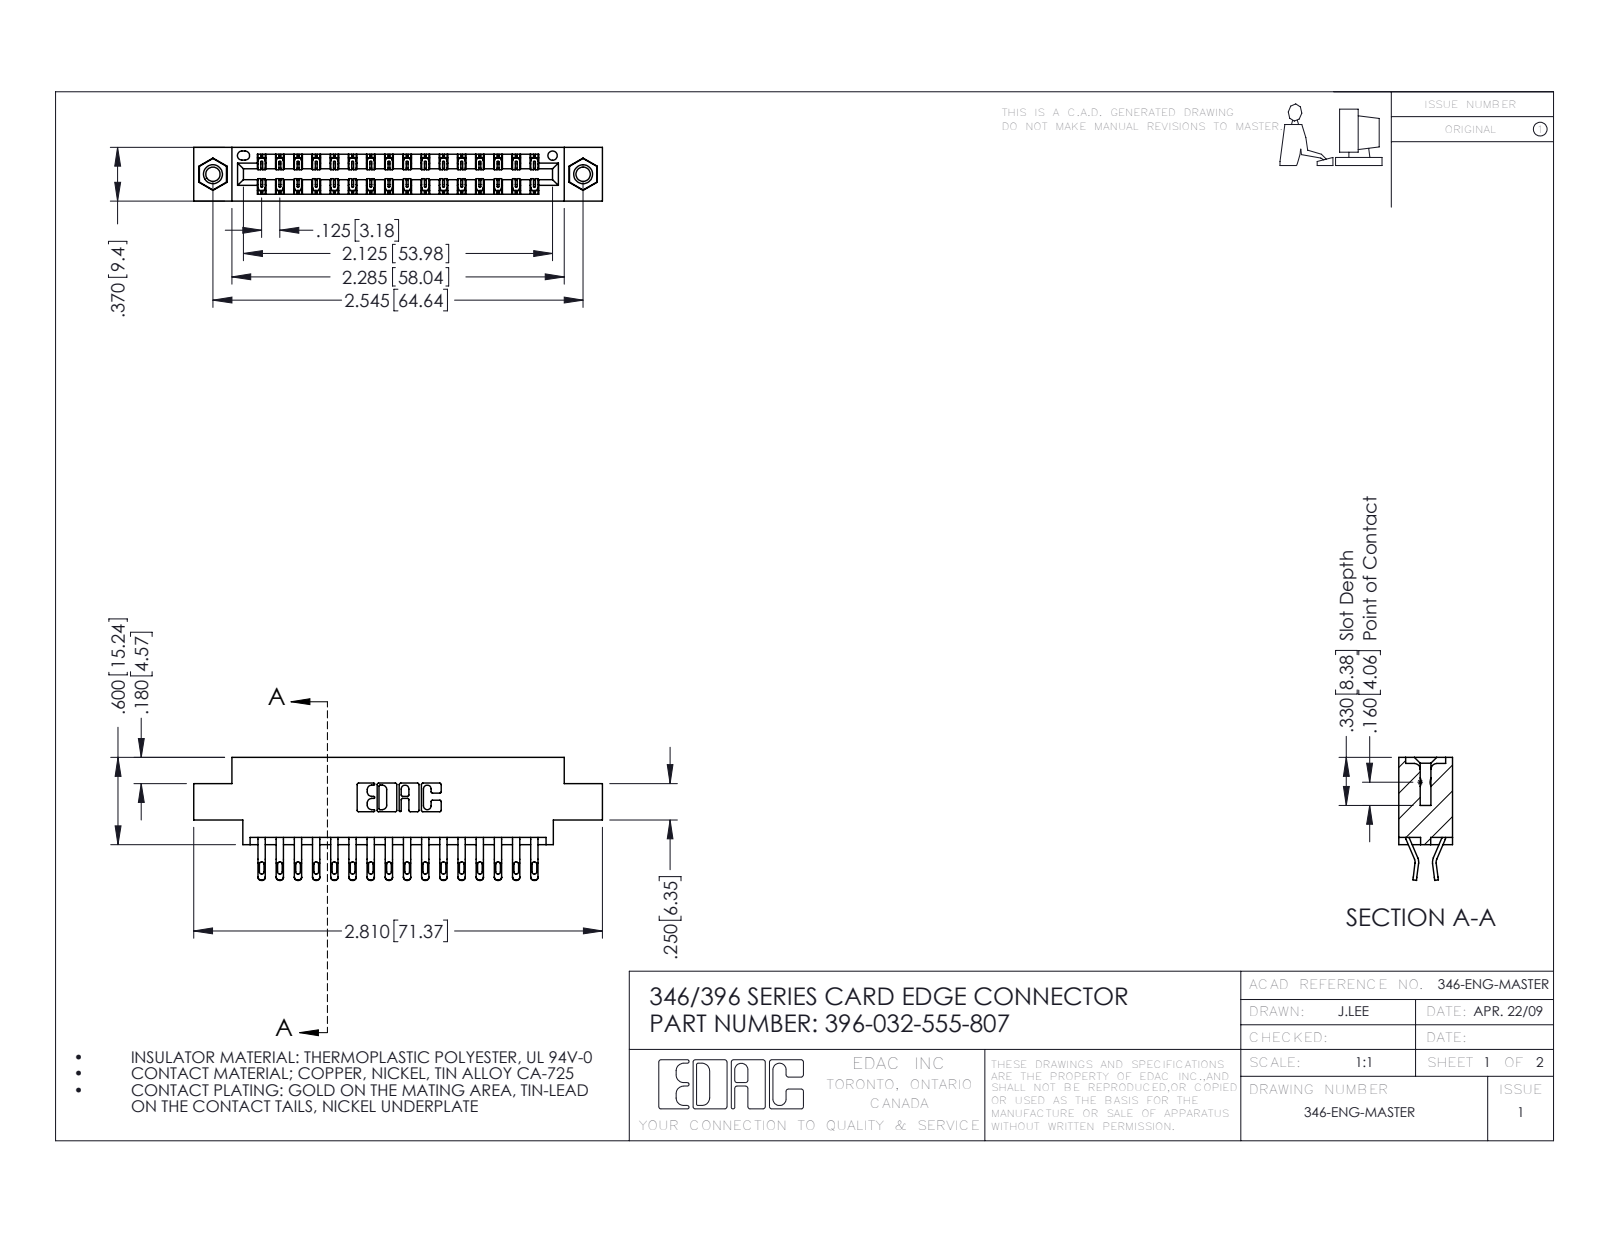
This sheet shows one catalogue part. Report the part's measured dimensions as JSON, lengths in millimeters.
{"part_name": "345-292-001_555 Tail; 346 Part_0.170 Offset - 0.156 Dia-TI; 396-032-555-807; 345-250-001_345-250-005-103", "step_written_by": "SolidWorks 2016 (CONFIG_CONTROL_DESIGN)", "units": "millimeters", "bodies": {"solids": 35, "faces": 2042, "planar": 1168, "cylindrical": 858, "other": 16}, "overall_size": [71.4, 21.5, 9.4], "volume_mm3": 6690, "surface_area_mm2": 9323, "round_holes": [[2.5, 2], [3.2, 2], [4, 2], [1.6, 1]], "round_bosses_or_shafts": [[3.9, 2]], "partial_cylinders_radius": [[0.4, 64], [0.5, 64], [0.2, 48], [0.3, 22], [0.2, 6], [0.8, 6], [0.7, 3], [0.3, 2]], "face_to_face_distances": [1.2, 8.2, 9.4, 6.4, 0.6, 1.8, 7.6, 7, 5.6, 3.8], "hole_center_spacings": [6.2, 59.4, 64.6]}
